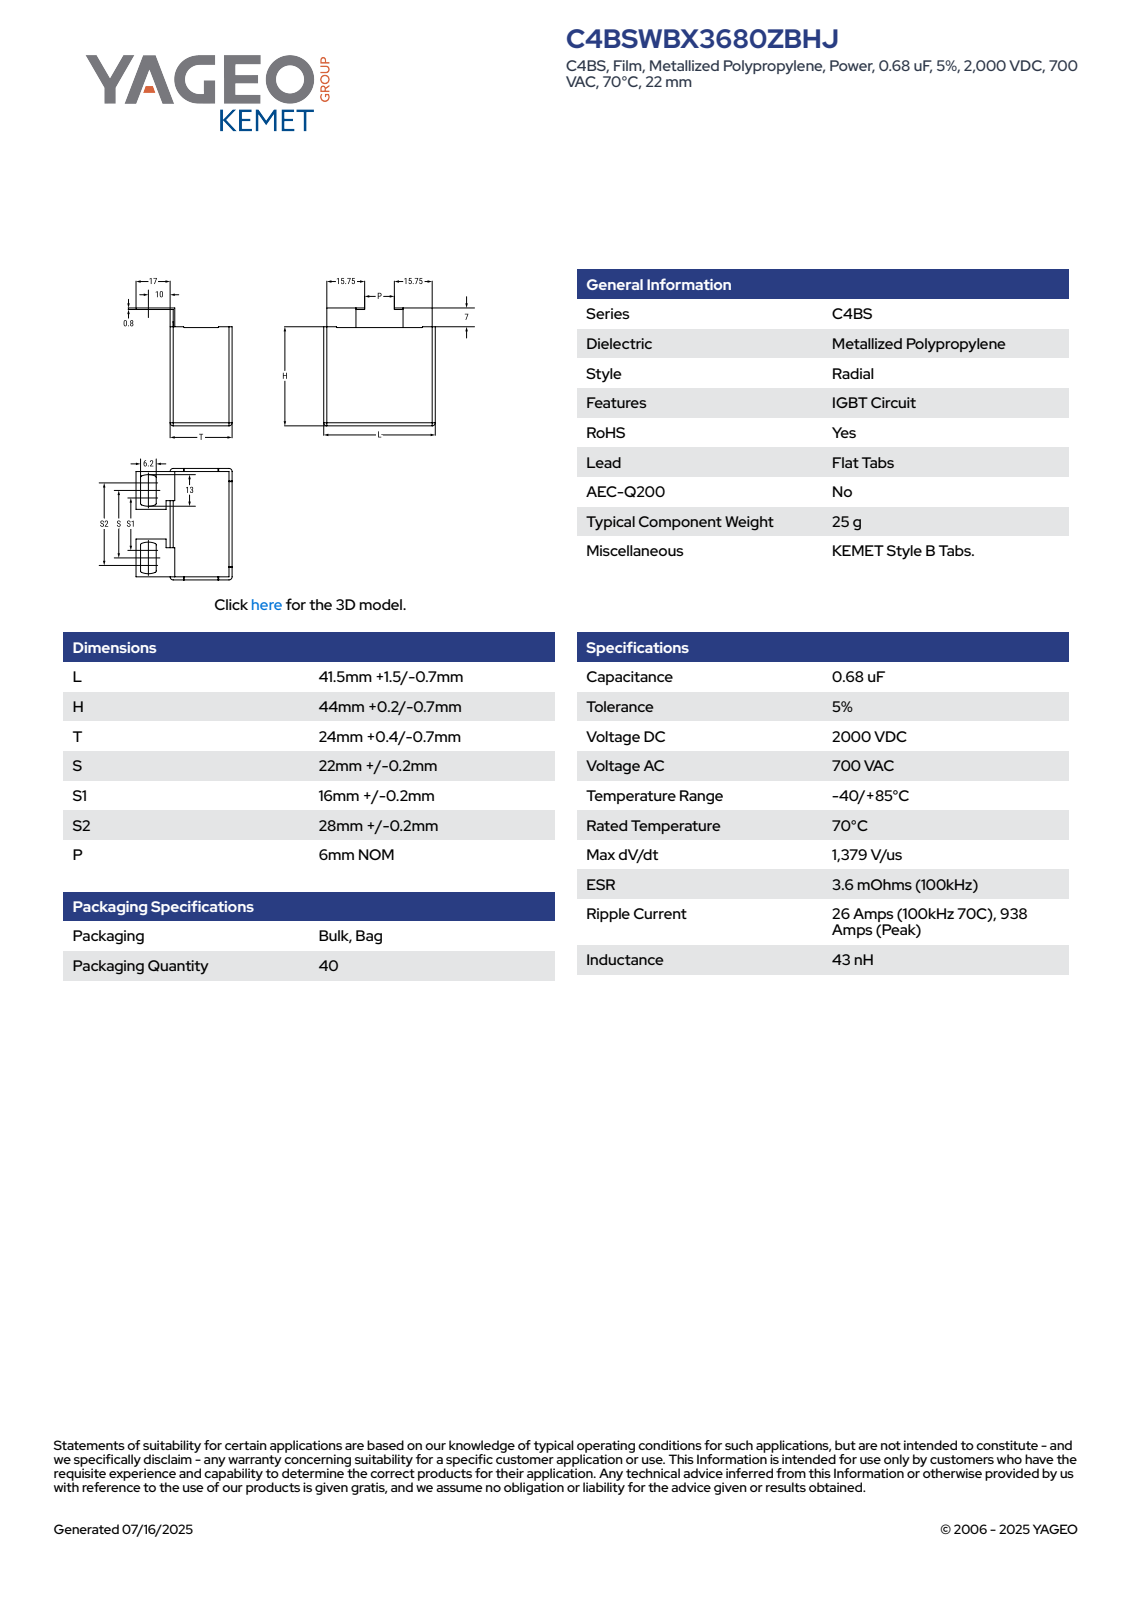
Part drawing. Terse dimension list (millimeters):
name: CFP_C4BB_41.5X44X24_L43.5H44.2T24.4S22.2
written by: SolidWorks 2014 (AUTOMOTIVE_DESIGN)
unit: mm
bodies: 4 solids, 93 faces (85 planar, 8 cylindrical, 0 other)
size: 51.2 × 43.5 × 41.4
volume: 47 449 mm³; area: 9 714 mm²
rounds: 4× R4.6, 2× R0.2
face distances: 24.4, 43.5, 44.2, 0.8, 7, 51.2, 6.2, 50.4, 22.4, 2
